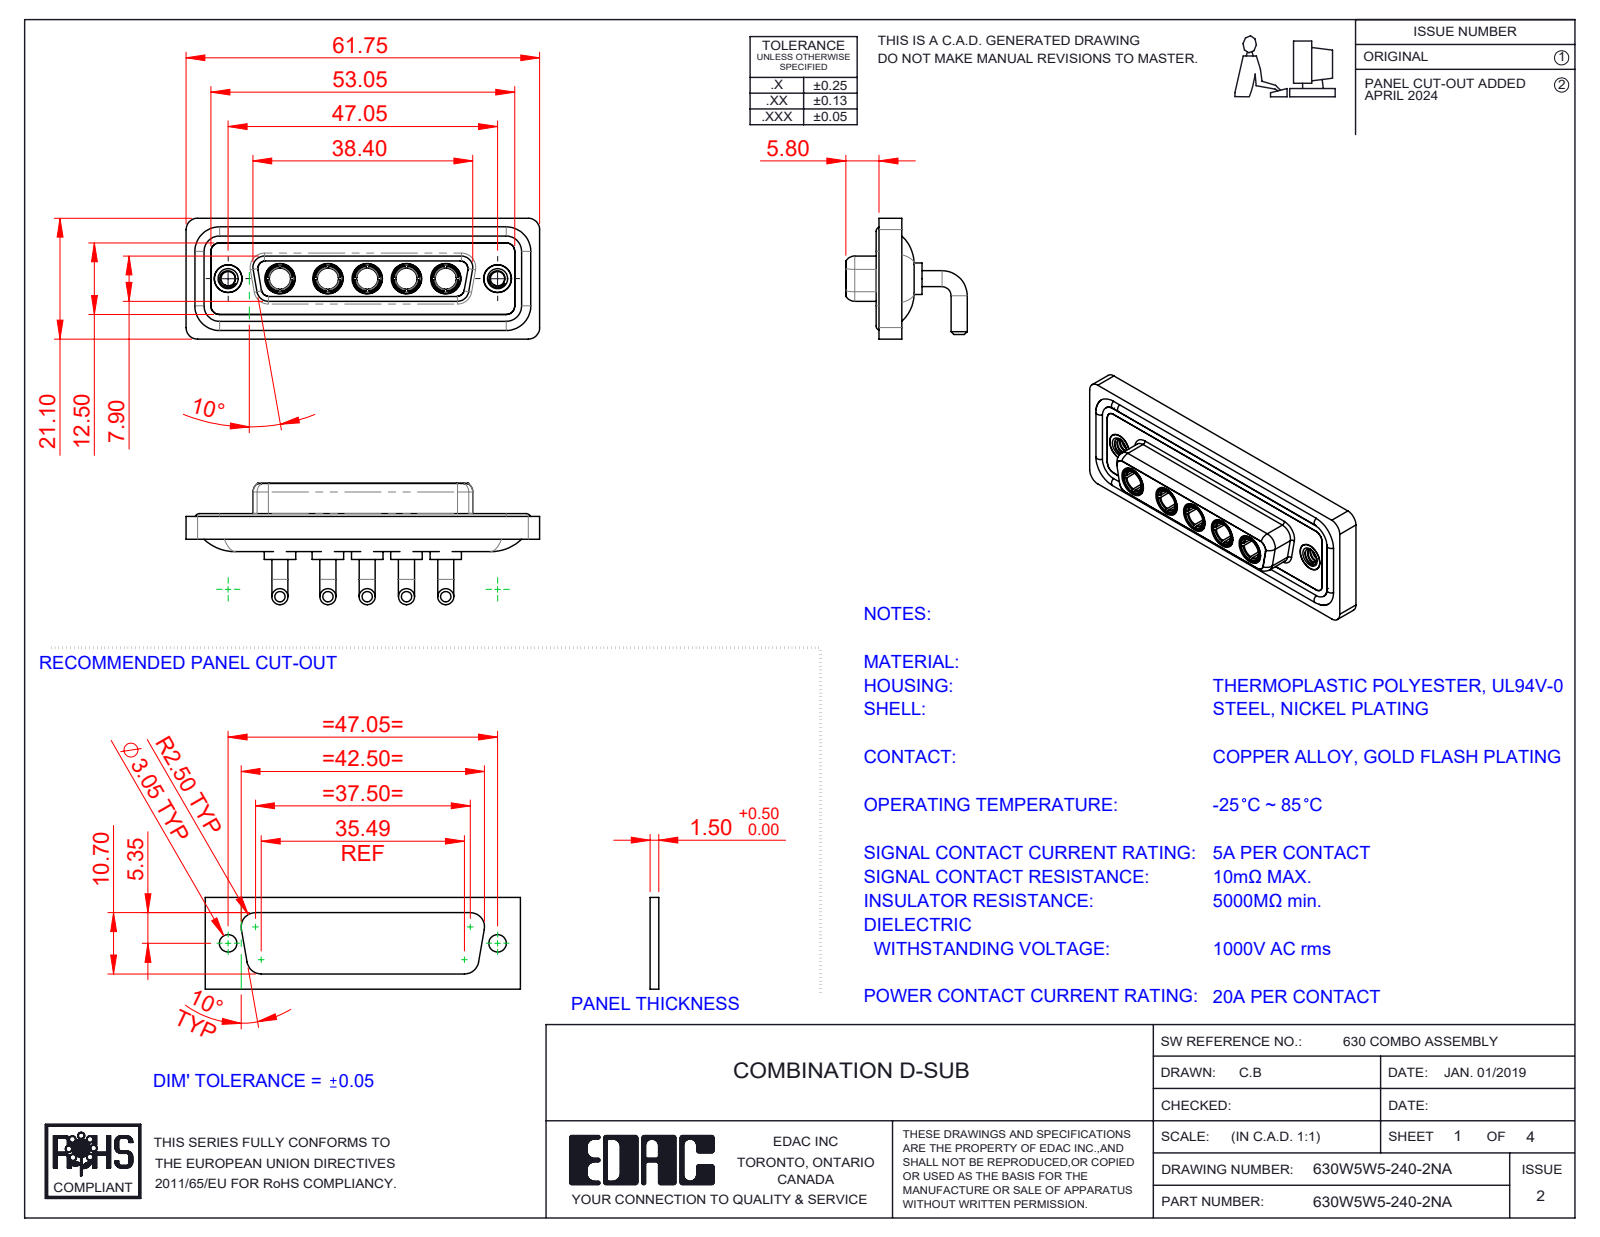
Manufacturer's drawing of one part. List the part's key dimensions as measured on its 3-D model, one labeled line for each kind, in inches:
Part name (STEP PRODUCT): 630Combo Housing_5W5; 630W5W5-140-2NA; 630Combo Waterproof Housing_25 Contacts; 630Combo Shell Front_25 Contacts (+3 more)
STEP written by: SolidWorks 2023 (CONFIG_CONTROL_DESIGN)
Units: inches
Bodies: 17 solids, 770 faces (250 planar, 311 cylindrical, 209 other)
Overall size (bounding box): 2.431 × 0.835 × 0.831
Volume: 0.514 in³ · Surface area: 21.41 in²
Round holes (diameter × count): ⌀0.191 ×7, ⌀0.146 ×5, ⌀0.209 ×5, ⌀0.098 ×2, ⌀0.157 ×2, ⌀0.159 ×2, ⌀0.197 ×2
Round bosses / shafts (diameter × count): ⌀0.11 ×10, ⌀0.217 ×5, ⌀0.205 ×5, ⌀0.195 ×5, ⌀0.187 ×5, ⌀0.148 ×5, ⌀0.063 ×4, ⌀0.195 ×2
Partial cylindrical surfaces — rounded edges, fillets, slot ends (radius × count): R0.059 ×18, R0.079 ×18, R0.053 ×8, R0.063 ×8, R0.083 ×5, R0.01 ×4, R0.02 ×4, R0.024 ×4
Main face-to-face distances: 0.016, 0.071, 0.161, 0.043, 0.059, 0.098, 0.122, 0.146, 0.063, 0.114
Hole centre spacings: 0.27, 0.356, 1.496, 0.27, 0.33, 0.54, 0.541, 0.6
